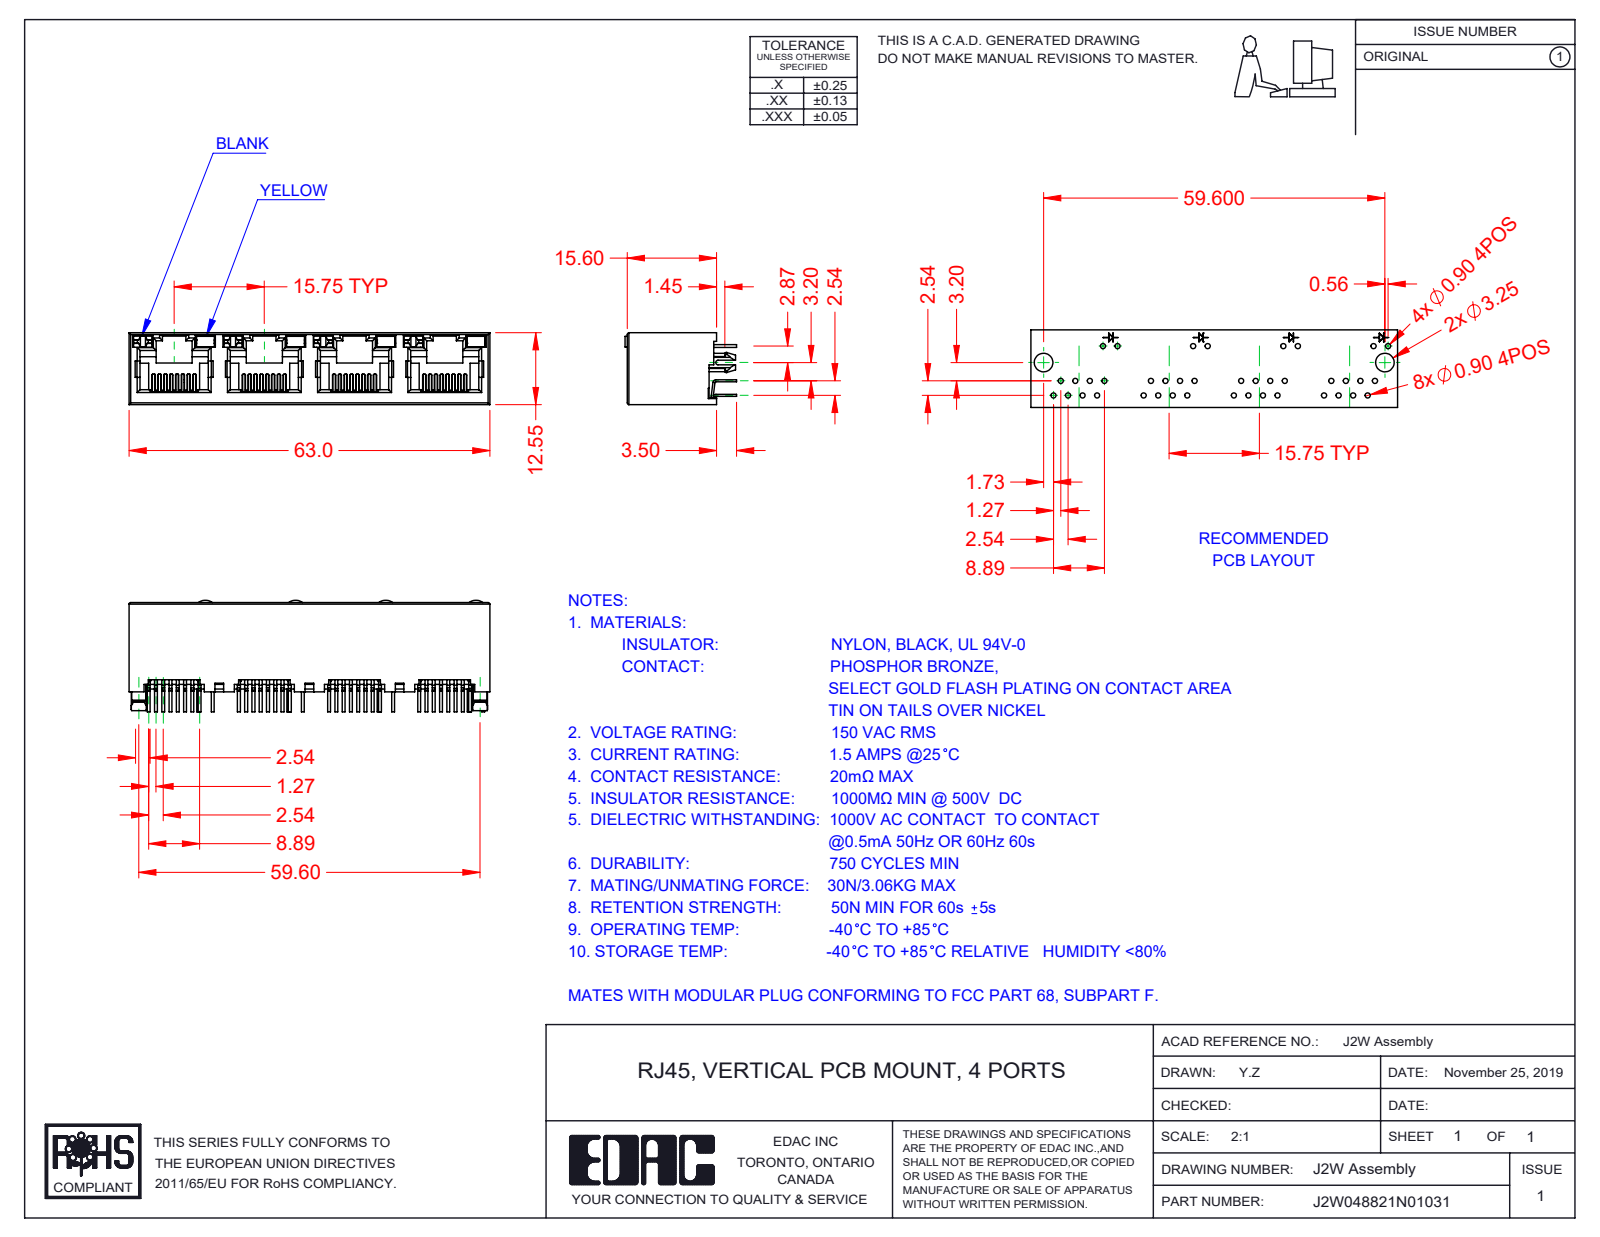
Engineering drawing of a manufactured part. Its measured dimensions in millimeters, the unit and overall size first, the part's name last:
Units: millimetres
Overall size (bounding box): 63 × 19.5 × 12.55
Partial cylindrical surfaces — rounded edges, fillets, slot ends (radius × count): R0.15 ×64, R0.2 ×29, R0.5 ×28, R0.3 ×14, R0.45 ×8, R2 ×4, R0.25 ×2, R1.5 ×2
Main face-to-face distances: 12.55, 11.9, 0.65, 15.75, 0.36, 1.5, 0.78, 0.6, 11.3, 31.5
Volume: 5 212 mm³ · Surface area: 12 695 mm²
Bodies: 41 solids, 3007 faces (2508 planar, 441 cylindrical, 58 other)
Part name (STEP PRODUCT): 2W LED LH_0-Blank; 2W Insulator; 2W Contact Lock; 2W Contacts (+2 more)
STEP written by: SolidWorks 2020 (CONFIG_CONTROL_DESIGN)
